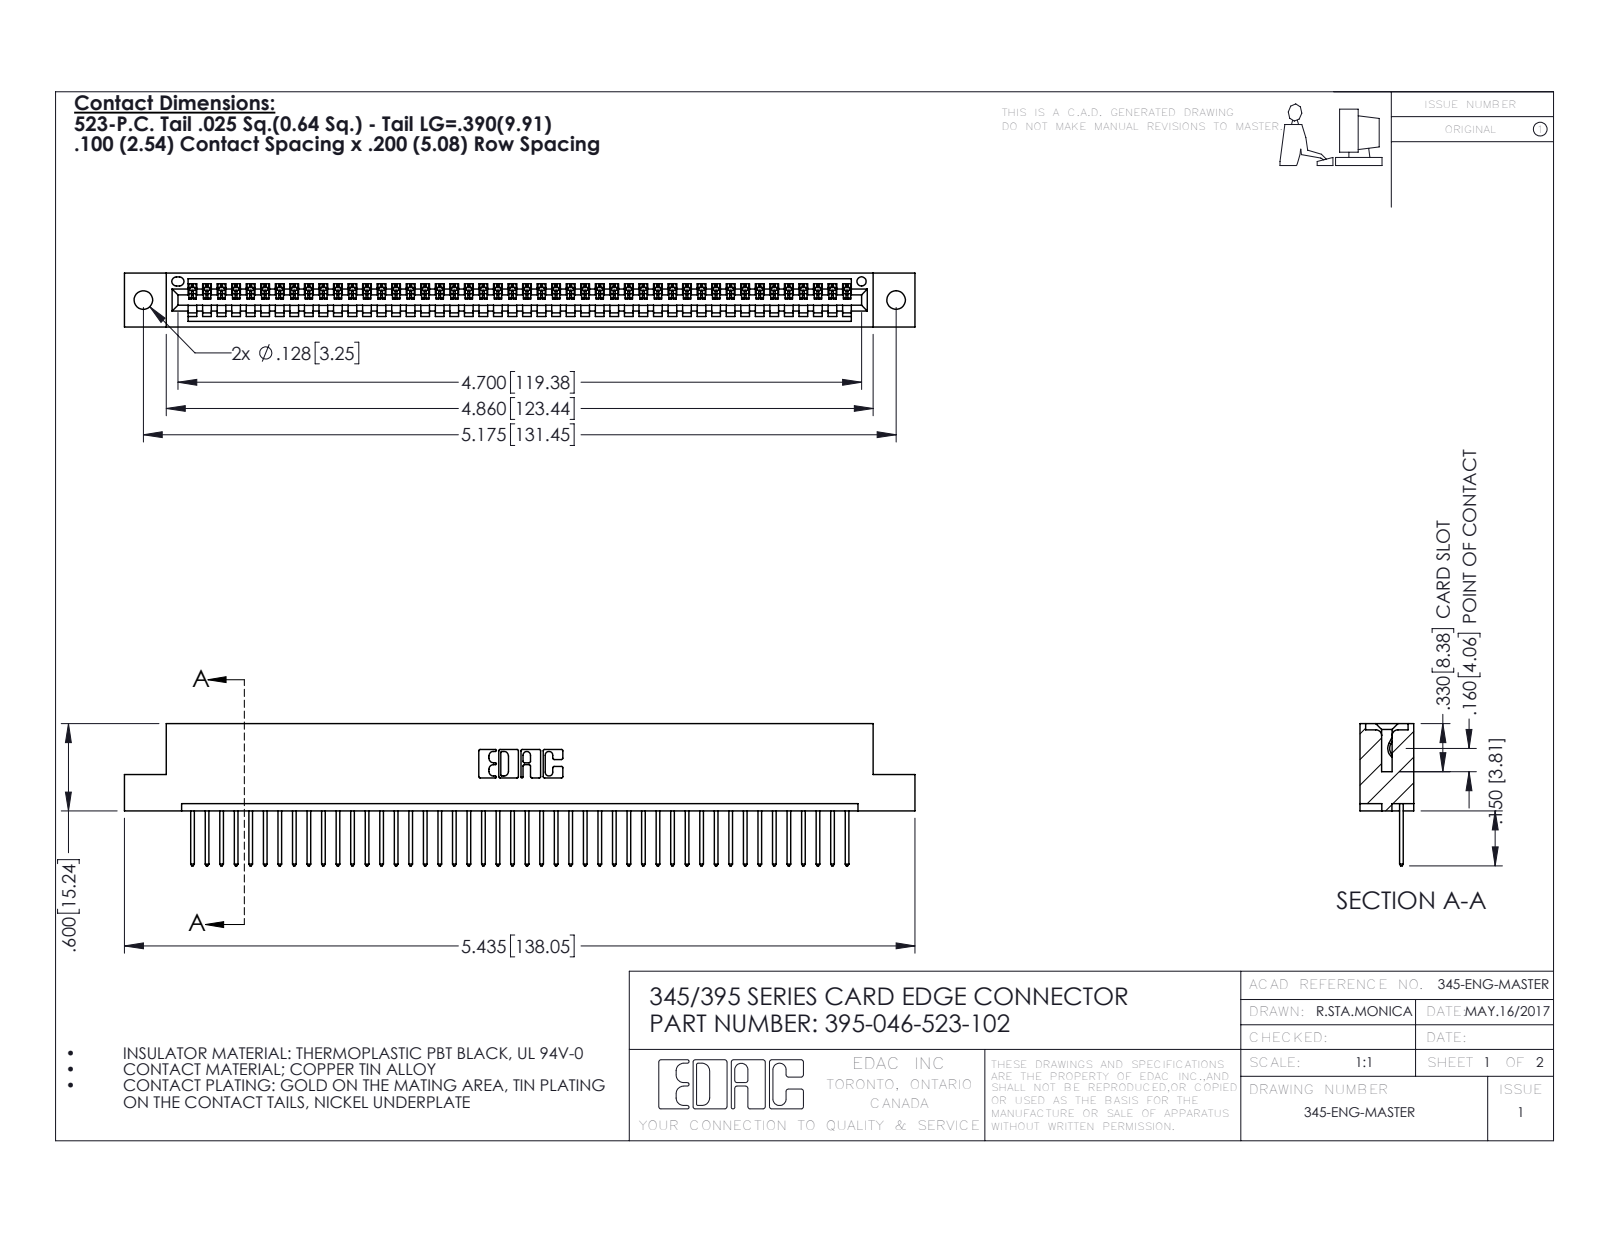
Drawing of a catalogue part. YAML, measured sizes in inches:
part_name: "395-046-523-102; 345-292-001_345-293-123; 345 Part_Flush Mounting Lugs - 0.128 Dia"
step_written_by: "SolidWorks 2016 (CONFIG_CONTROL_DESIGN)"
units: inches
bodies: {solids: 47, faces: 2794, planar: 1920, cylindrical: 874, other: 0}
overall_size: [5.435, 0.977, 0.37]
volume: 0.799
surface_area: 26.7
round_holes:
  - {diameter: 0.128, count: 2}
  - {diameter: 0.064, count: 1}
partial_cylinders:
  - {radius: 0.006, count: 92}
  - {radius: 0.01, count: 92}
  - {radius: 0.01, count: 22}
  - {radius: 0.007, count: 6}
  - {radius: 0.031, count: 6}
  - {radius: 0.026, count: 3}
  - {radius: 0.031, count: 2}
  - {radius: 0.04, count: 2}
face_to_face_distances: [0.298, 0.072, 0.37, 0.2, 0.098, 0.272, 0.025, 0.225, 0.149, 0.072]
hole_center_spacings: [0.27, 4.939, 5.175]
